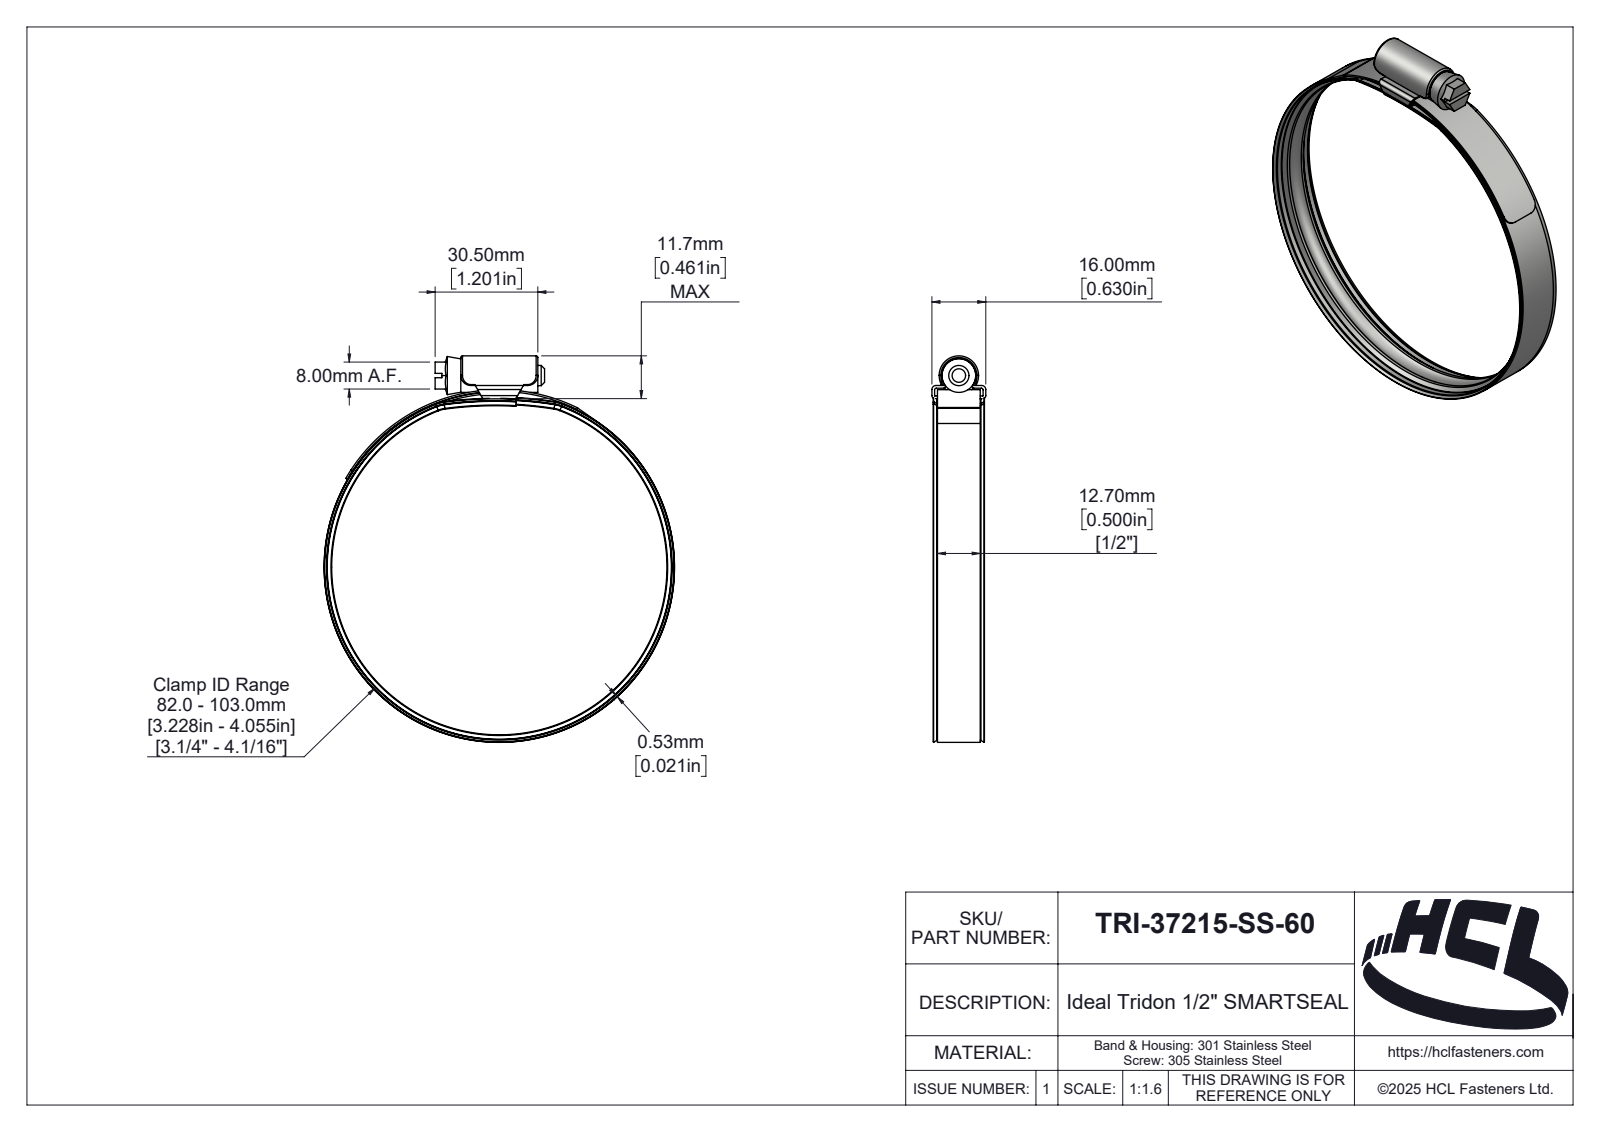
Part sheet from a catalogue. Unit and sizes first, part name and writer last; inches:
Units: inches
Overall size (bounding box): 4.517 × 4.097 × 0.63
Round holes (diameter × count): ⌀4.031 ×1, ⌀4.055 ×1
Round bosses / shafts (diameter × count): ⌀4.097 ×1, ⌀4.047 ×1, ⌀0.394 ×1, ⌀0.236 ×1
Partial cylindrical surfaces — rounded edges, fillets, slot ends (radius × count): R0.02 ×6, R0.118 ×4, R0.004 ×2, R0.035 ×2, R0.047 ×2, R0.39 ×2, R0.398 ×2, R0.018 ×1
Main face-to-face distances: 0.031, 0.5, 0.122, 0.021, 0.091, 1.201, 0.154, 0.065, 0.565, 0.598
Volume: 0.411 in³ · Surface area: 37.69 in²
Bodies: 4 solids, 418 faces (42 planar, 119 cylindrical, 257 other)
Part name (STEP PRODUCT): TRI-37215-SS-60
STEP written by: SolidWorks 2025 (AUTOMOTIVE_DESIGN)
